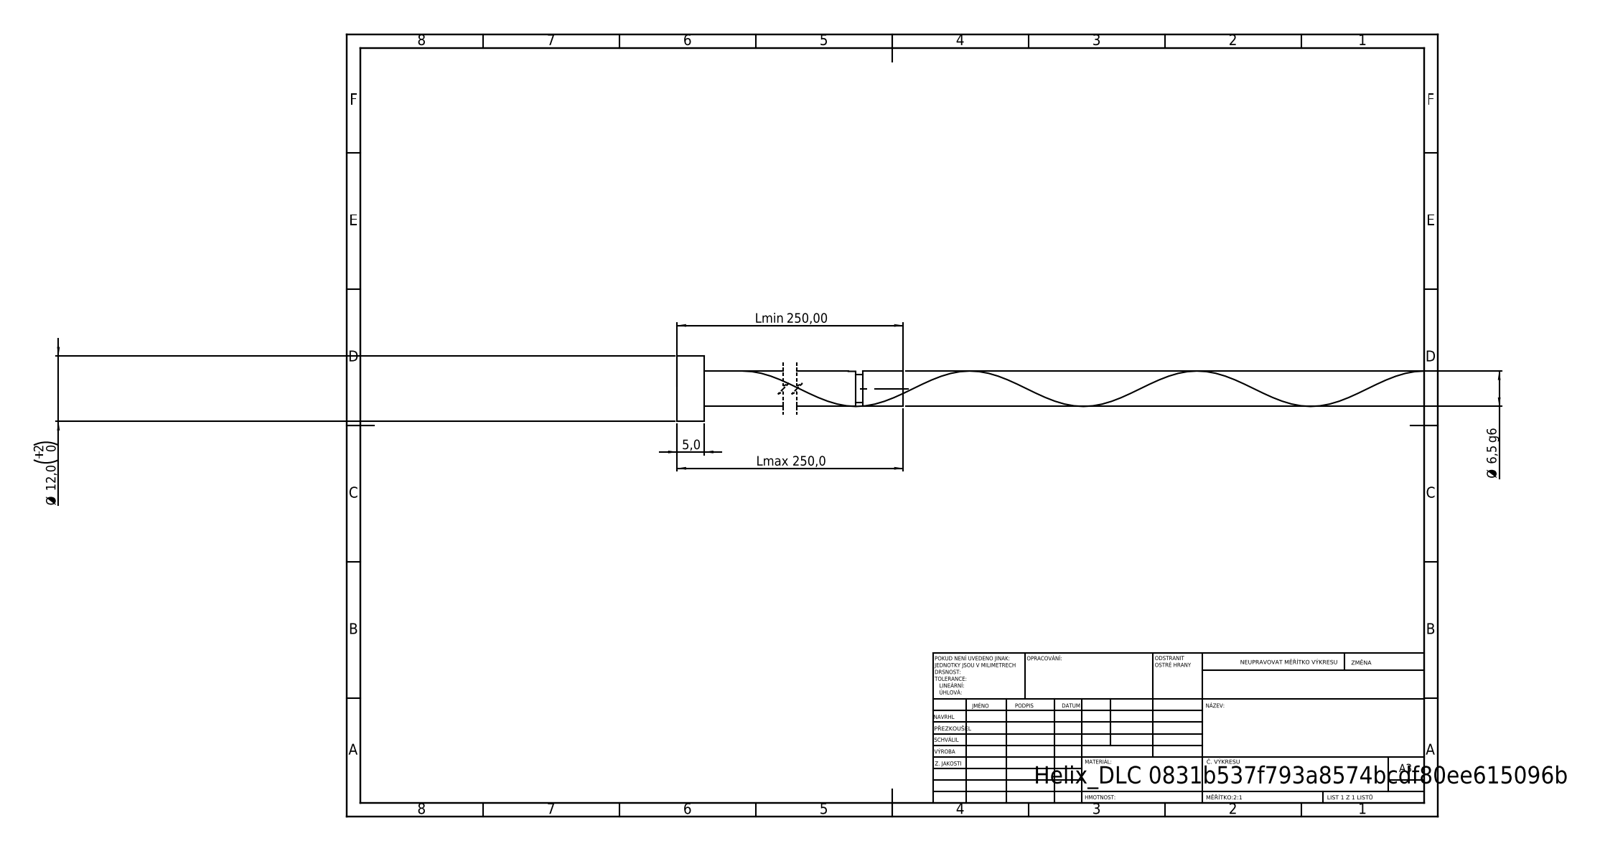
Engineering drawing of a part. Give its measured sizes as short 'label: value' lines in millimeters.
written by: SolidWorks 2019 (CONFIG_CONTROL_DESIGN)
unit: mm
bodies: 1 solid, 21 faces (6 planar, 14 cylindrical, 1 other)
size: 250 × 12 × 12
volume: 8 600 mm³; area: 5 525 mm²
bosses: 1× ⌀12, 1× ⌀6.5, 1× ⌀5.2
face distances: 5, 250, 245, 242.57, 237.57, 7.43, 241.27, 236.27, 1.3, 8.73
